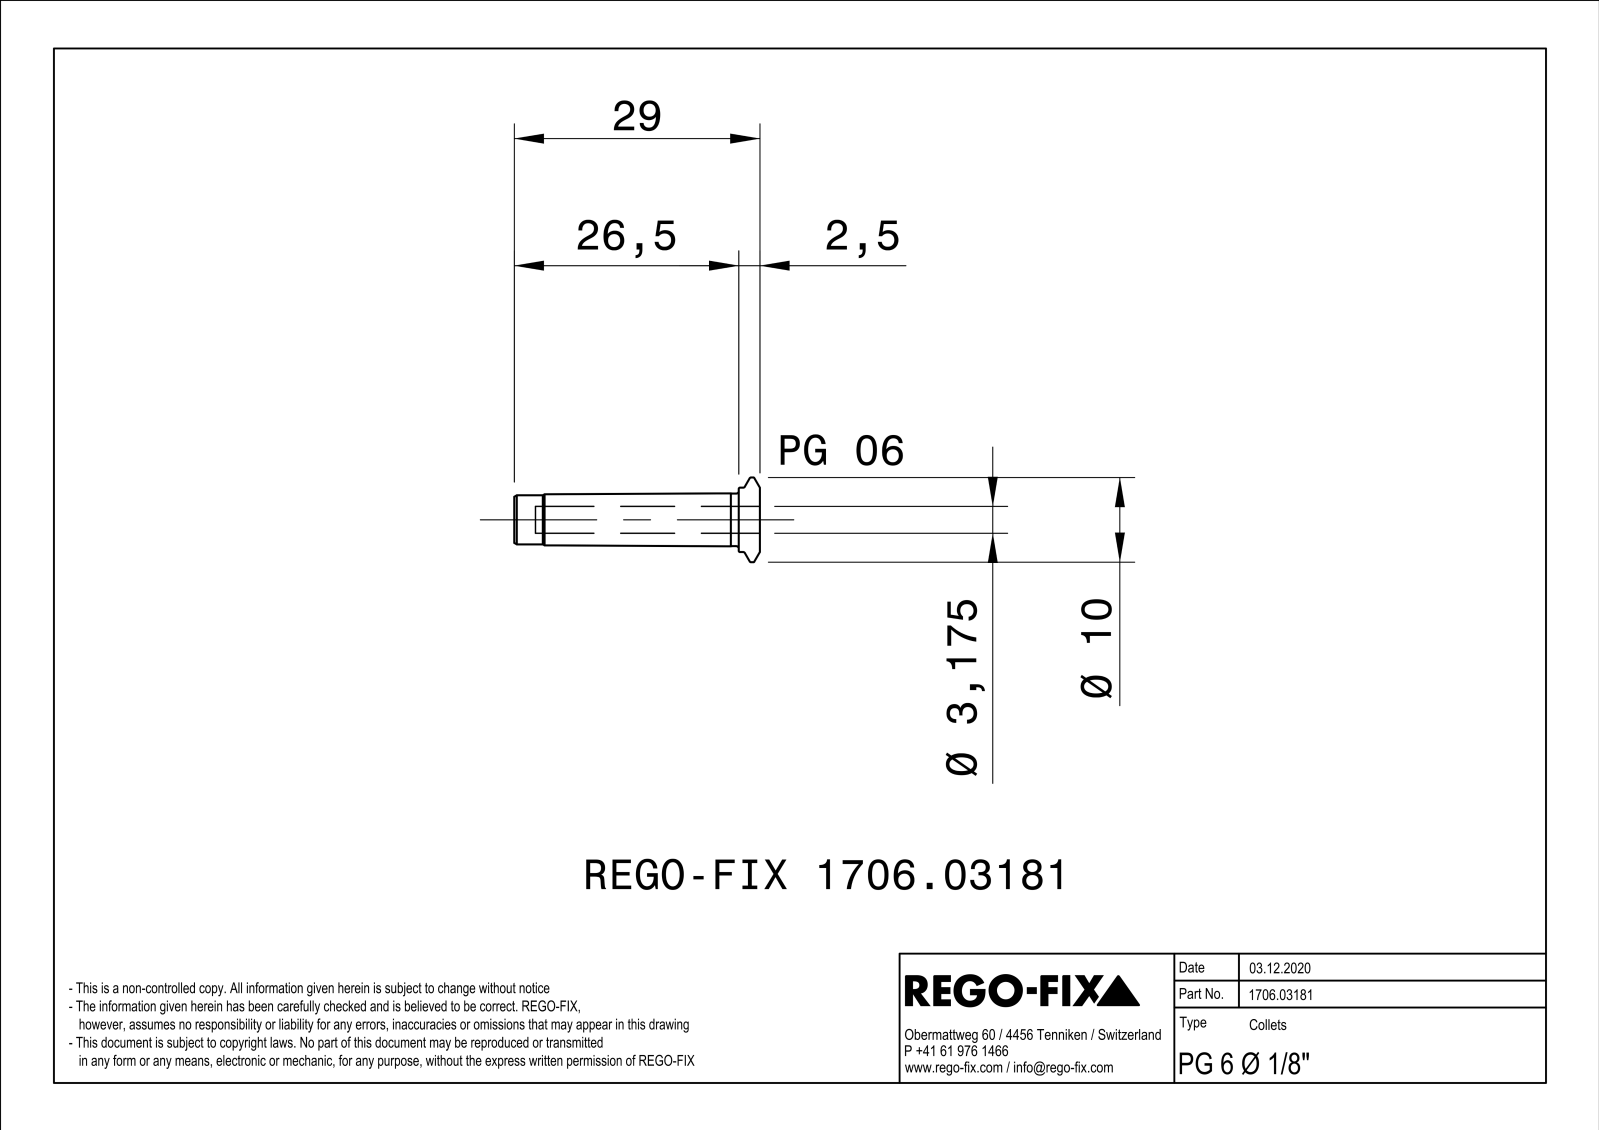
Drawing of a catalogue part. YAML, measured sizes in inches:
part_name: "NOCUT"
step_written_by: "SIEMENS PLM Software Solid Edge ST10 (AUTOMOTIVE_DESIGN)"
units: inches
bodies: {solids: 1, faces: 61, planar: 17, cylindrical: 12, other: 32}
overall_size: [1.142, 0.394, 0.393]
volume: 0.04
surface_area: 1.702
round_holes:
  - {diameter: 0.125, count: 1}
  - {diameter: 0.136, count: 1}
round_bosses_or_shafts:
  - {diameter: 0.394, count: 1}
  - {diameter: 0.299, count: 1}
  - {diameter: 0.244, count: 1}
  - {diameter: 0.228, count: 1}
face_to_face_distances: [0.018, 0.018, 1.142, 0.098, 1.043]
